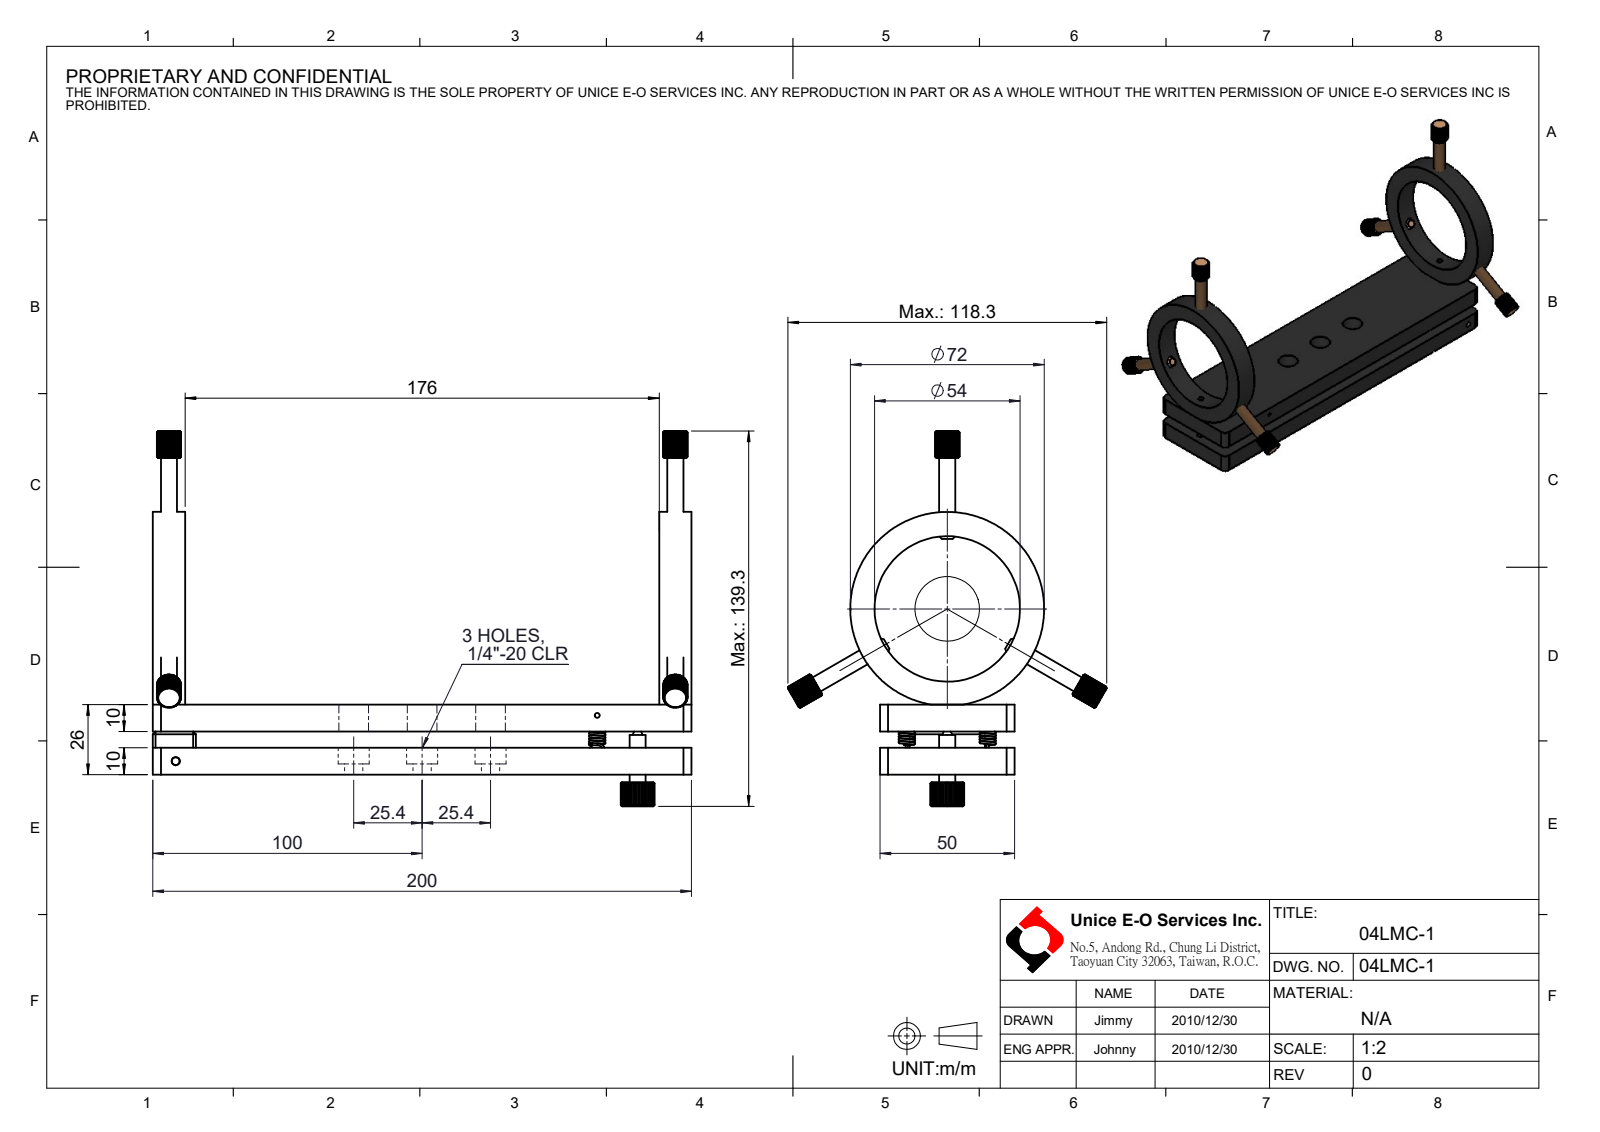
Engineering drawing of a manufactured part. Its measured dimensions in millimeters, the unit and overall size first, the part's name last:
Units: millimetres
Overall size (bounding box): 200 × 139.25 × 118.31
Round holes (diameter × count): ⌀5 ×7, ⌀6.76 ×3, ⌀11 ×3, ⌀11.51 ×3, ⌀1.25 ×2, ⌀3.3 ×2, ⌀4.5 ×2, ⌀6 ×2, ⌀8 ×2, ⌀1.8 ×1, ⌀3 ×1, ⌀4.1 ×1
Round bosses / shafts (diameter × count): ⌀6 ×7, ⌀1.6 ×2, ⌀0.8 ×2, ⌀72 ×1
Partial cylindrical surfaces — rounded edges, fillets, slot ends (radius × count): R0.25 ×40, R3 ×8, R4.5 ×6, R1 ×4, R2 ×1, R6.25 ×1
Main face-to-face distances: 10, 16, 26, 6, 50, 12, 188, 200, 176, 40
Hole centre spacings: 188, 21.21, 25.4, 32.65, 42.35, 66.71, 68.6, 91.64
Volume: 244 815 mm³ · Surface area: 81 210 mm²
Bodies: 17 solids, 1213 faces (644 planar, 494 cylindrical, 75 other)
Part name (STEP PRODUCT): 04LMC-1
STEP written by: SolidWorks 2016 (CONFIG_CONTROL_DESIGN)
